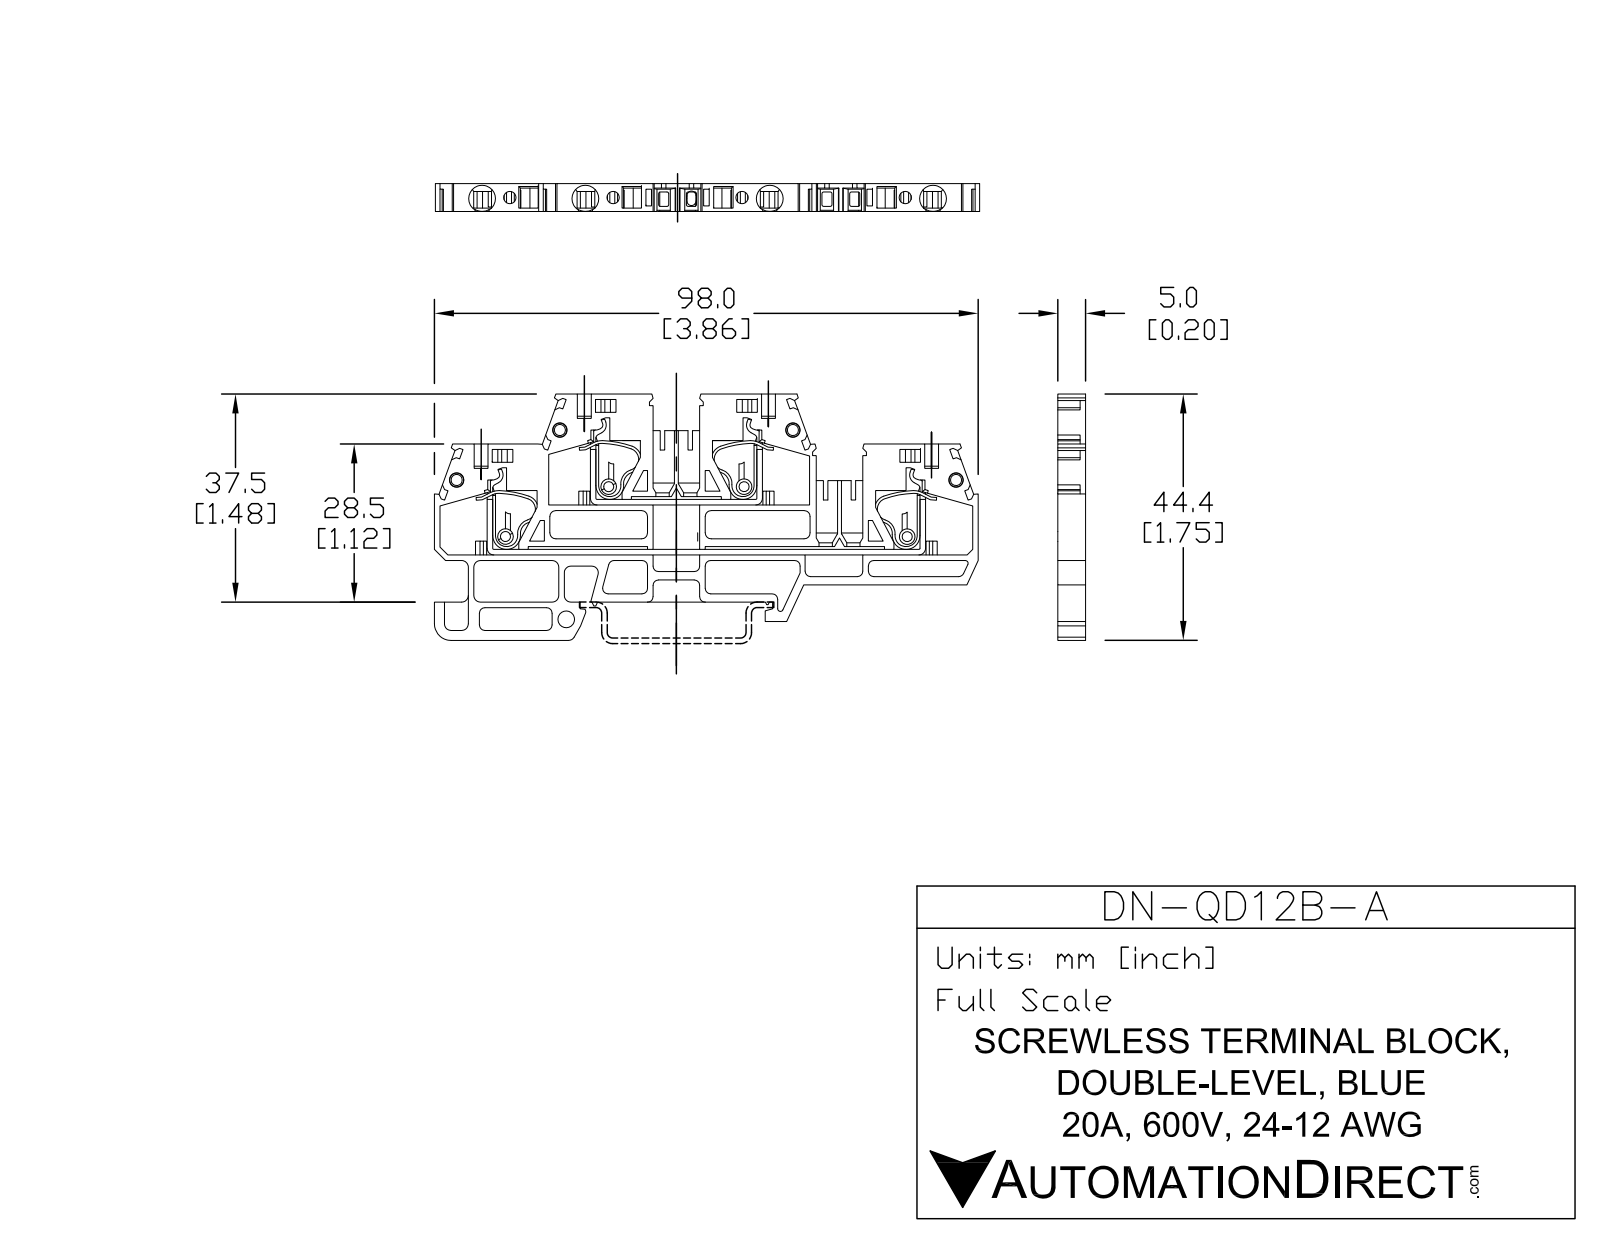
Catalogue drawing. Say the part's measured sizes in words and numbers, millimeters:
The part is named "DN-QD12B-A". Its 3-D file was written by "SolidWorks 2017 (AUTOMOTIVE_DESIGN)". It is 1 solid with 713 faces: 536 planar, 129 cylindrical and 48 other. Overall it measures 98 by 44.4 by 5 millimeters. Its volume is 6 540 cubic millimeters and its surface area 12 540 square millimeters. Round holes: 4 of diameter 2.2, 4 of diameter 2.6, 4 of diameter 4.8, 1 of diameter 3. Round bosses or shafts: 4 of diameter 2.8. Partial cylindrical surfaces (rounded edges, fillets, slot ends): 23 of radius 1, 12 of radius 1.2, 8 of radius 1.1, 4 of radius 0.5, 4 of radius 0.7, 4 of radius 1.4, 1 of radius 0.3, 1 of radius 3. The main face-to-face distances are 5, 1, 0.8, 4.2, 2, 3, 2.9, 0.7, 10, 1.5. The hole center spacings are 5, 18.6, 28.2, 29.4, 46.8, 57.6, 76.2, 13.6.
